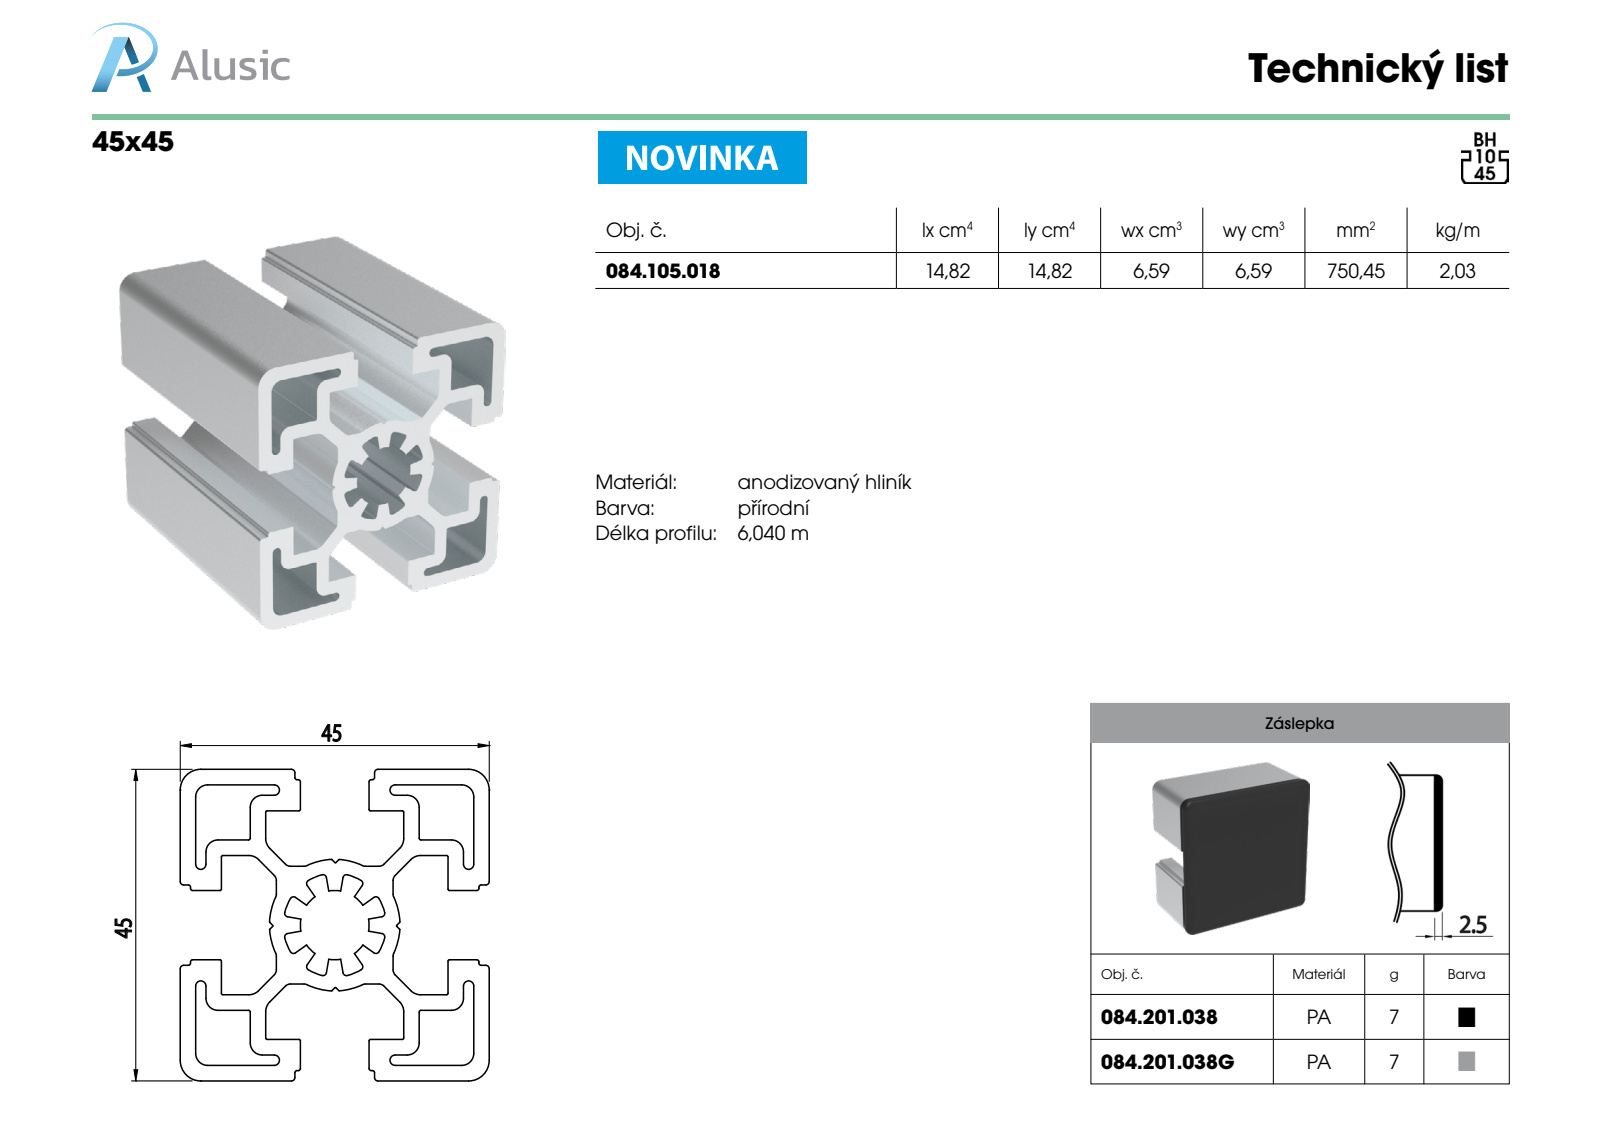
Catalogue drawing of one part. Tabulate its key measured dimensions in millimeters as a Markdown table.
| quantity | value |
| --- | --- |
| part name | 084.105.018 |
| STEP written by | SolidWorks 2018 (AUTOMOTIVE_DESIGN) |
| units | millimeters |
| bodies | 1 solid, 268 faces (114 planar, 154 cylindrical, 0 other) |
| overall size | 100 × 45 × 45 |
| volume | 75 045 mm³ |
| surface area | 62 132 mm² |
| partial cylindrical surfaces (radius × count) | 0.5 × 24, 0.2 × 16, 0.3 × 16, 1 × 16, 0.1 × 12, 1.75 × 12, 0.75 × 8, 2 × 8 |
| main face-to-face distances | 2.25, 42.75, 10.2, 32.55, 45, 3.75, 39, 28.8, 6.45, 40.5 |
